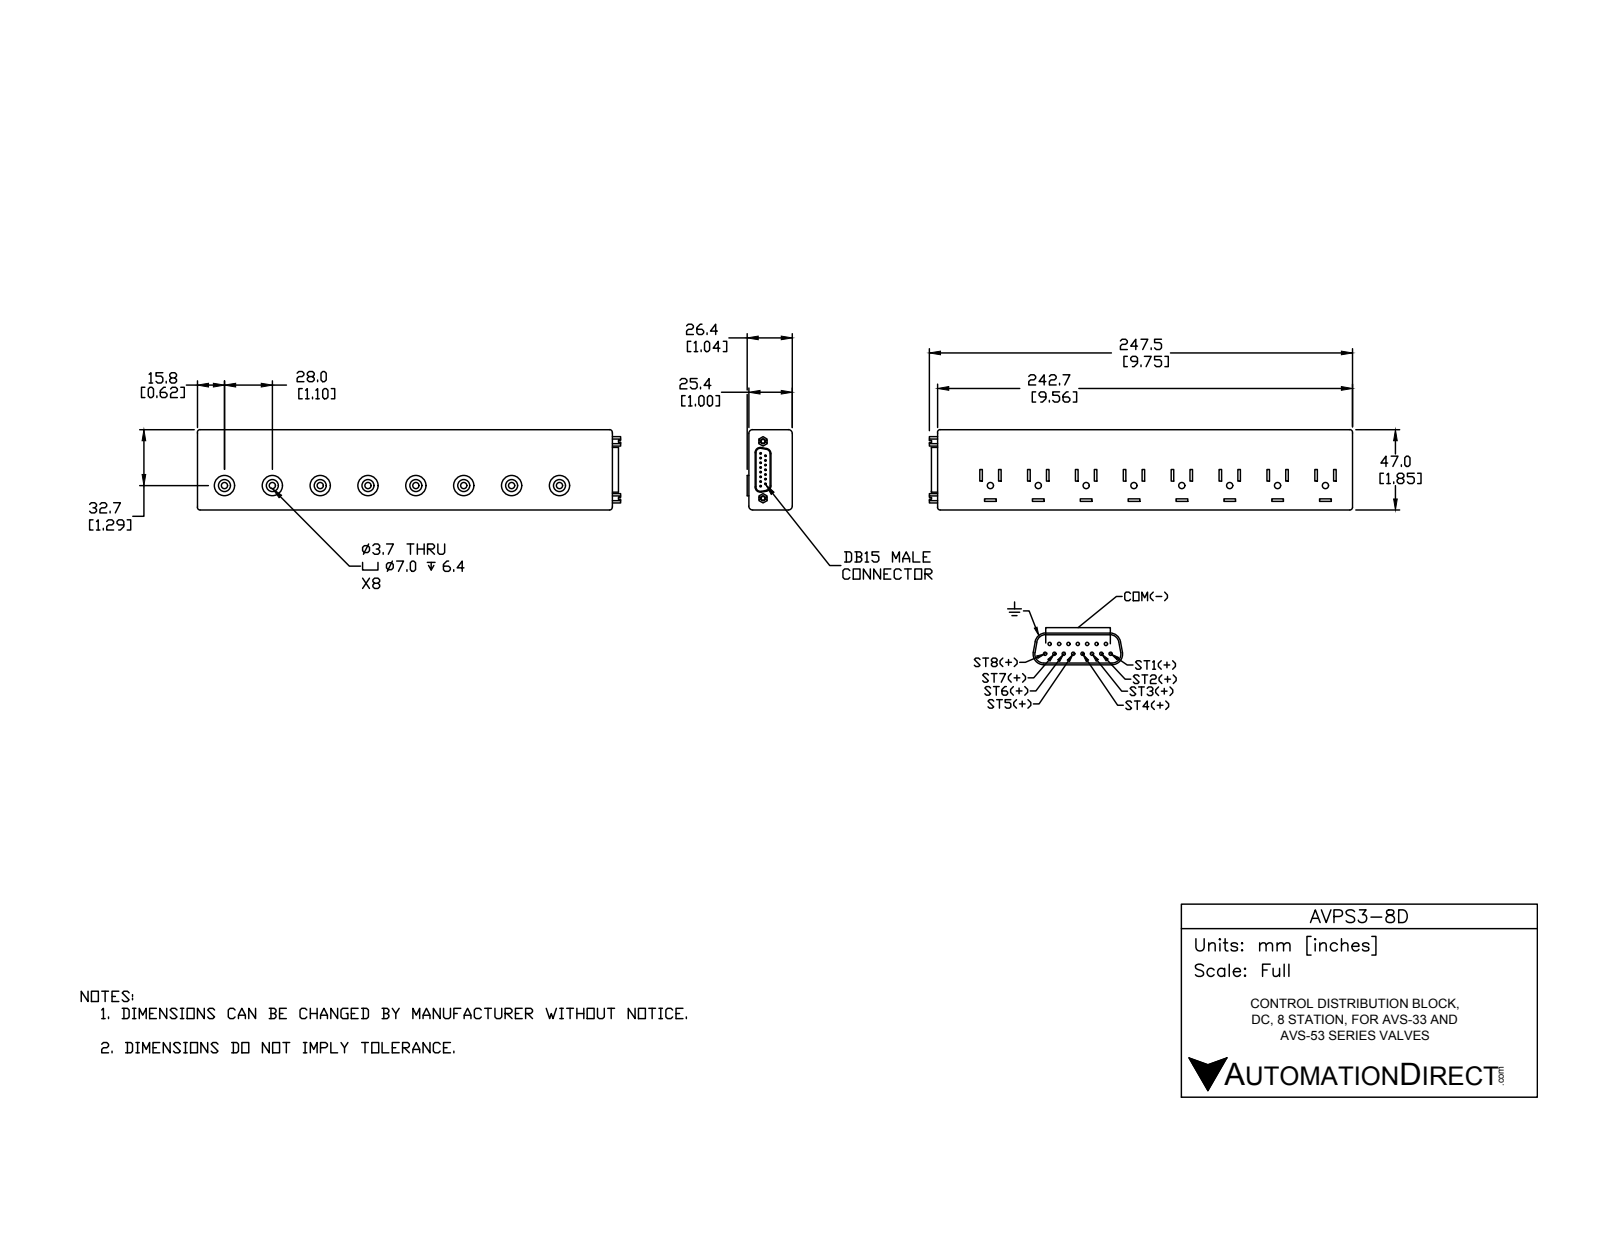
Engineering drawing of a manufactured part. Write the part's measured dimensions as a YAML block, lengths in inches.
part_name: "AVPS3-8D"
step_written_by: "SolidWorks 2016 (AUTOMOTIVE_DESIGN)"
units: inches
bodies: {solids: 1, faces: 311, planar: 195, cylindrical: 104, other: 12}
overall_size: [9.743, 1.85, 1.04]
volume: 17.32
surface_area: 66.88
round_holes:
  - {diameter: 0.145, count: 8}
  - {diameter: 0.275, count: 8}
  - {diameter: 0.089, count: 2}
round_bosses_or_shafts:
  - {diameter: 0.039, count: 15}
  - {diameter: 0.469, count: 8}
partial_cylinders:
  - {radius: 0.062, count: 8}
  - {radius: 0.09, count: 4}
  - {radius: 0.102, count: 4}
  - {radius: 0.122, count: 4}
face_to_face_distances: [1, 1.85, 9.554, 0.04, 1.04, 0.059, 1.102, 0.25, 0.79, 2.204]
hole_center_spacings: [1.102, 2.204, 4.408, 3.306, 5.51, 2.204, 3.306, 6.612]
